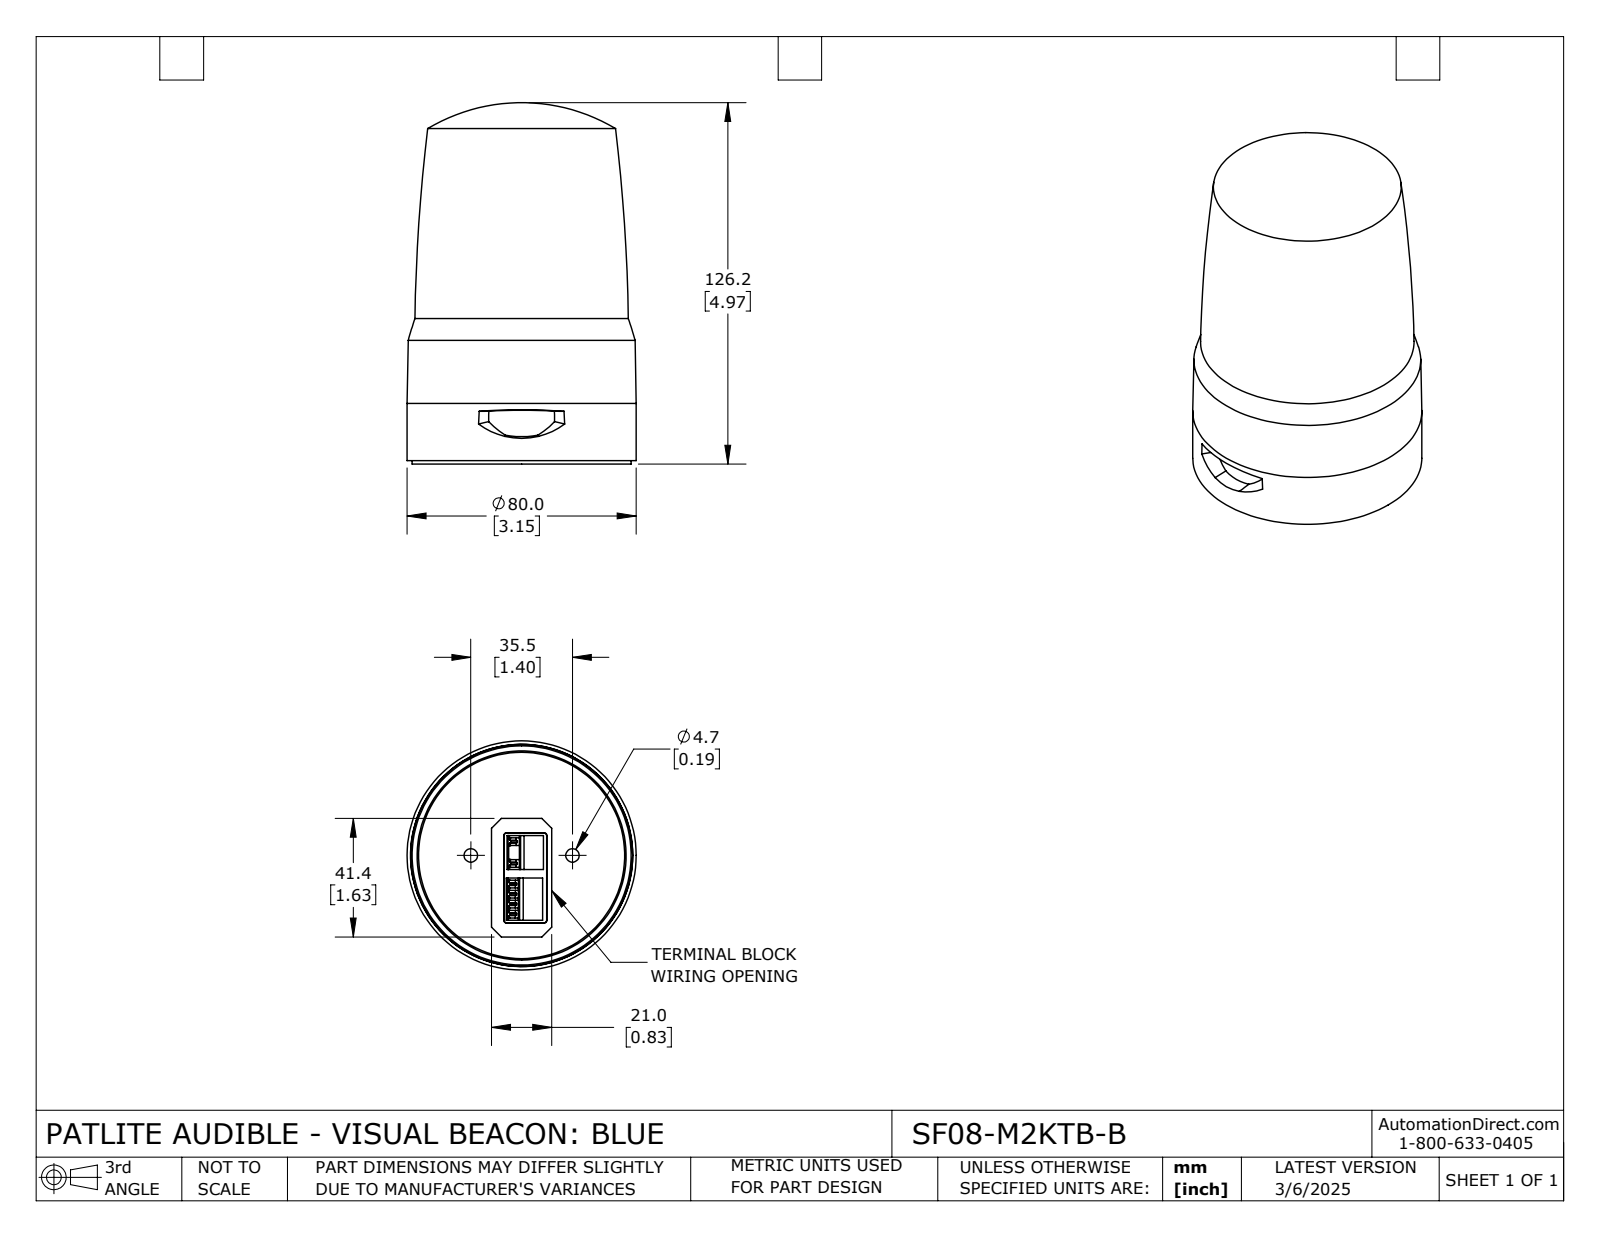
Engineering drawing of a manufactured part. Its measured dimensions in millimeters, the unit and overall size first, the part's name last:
Units: millimetres
Overall size (bounding box): 126.2 × 80 × 80
Round holes (diameter × count): ⌀4.7 ×2, ⌀12.2 ×2, ⌀73 ×1
Round bosses / shafts (diameter × count): ⌀80 ×1, ⌀76.5 ×1, ⌀74.6 ×1, ⌀72 ×1
Partial cylindrical surfaces — rounded edges, fillets, slot ends (radius × count): R1 ×4, R0.3 ×2, R34.6 ×1, R35 ×1
Main face-to-face distances: 15.7, 6.3, 9.4, 3, 5.1, 14.5, 3.15, 6.15, 1.3, 12.45
Hole centre spacings: 17.75, 35.5
Volume: 488 153 mm³ · Surface area: 54 584 mm²
Bodies: 2 solids, 262 faces (168 planar, 32 cylindrical, 62 other)
Part name (STEP PRODUCT): SF08-M2KTB-B
STEP written by: SolidWorks 2024 (CONFIG_CONTROL_DESIGN)
